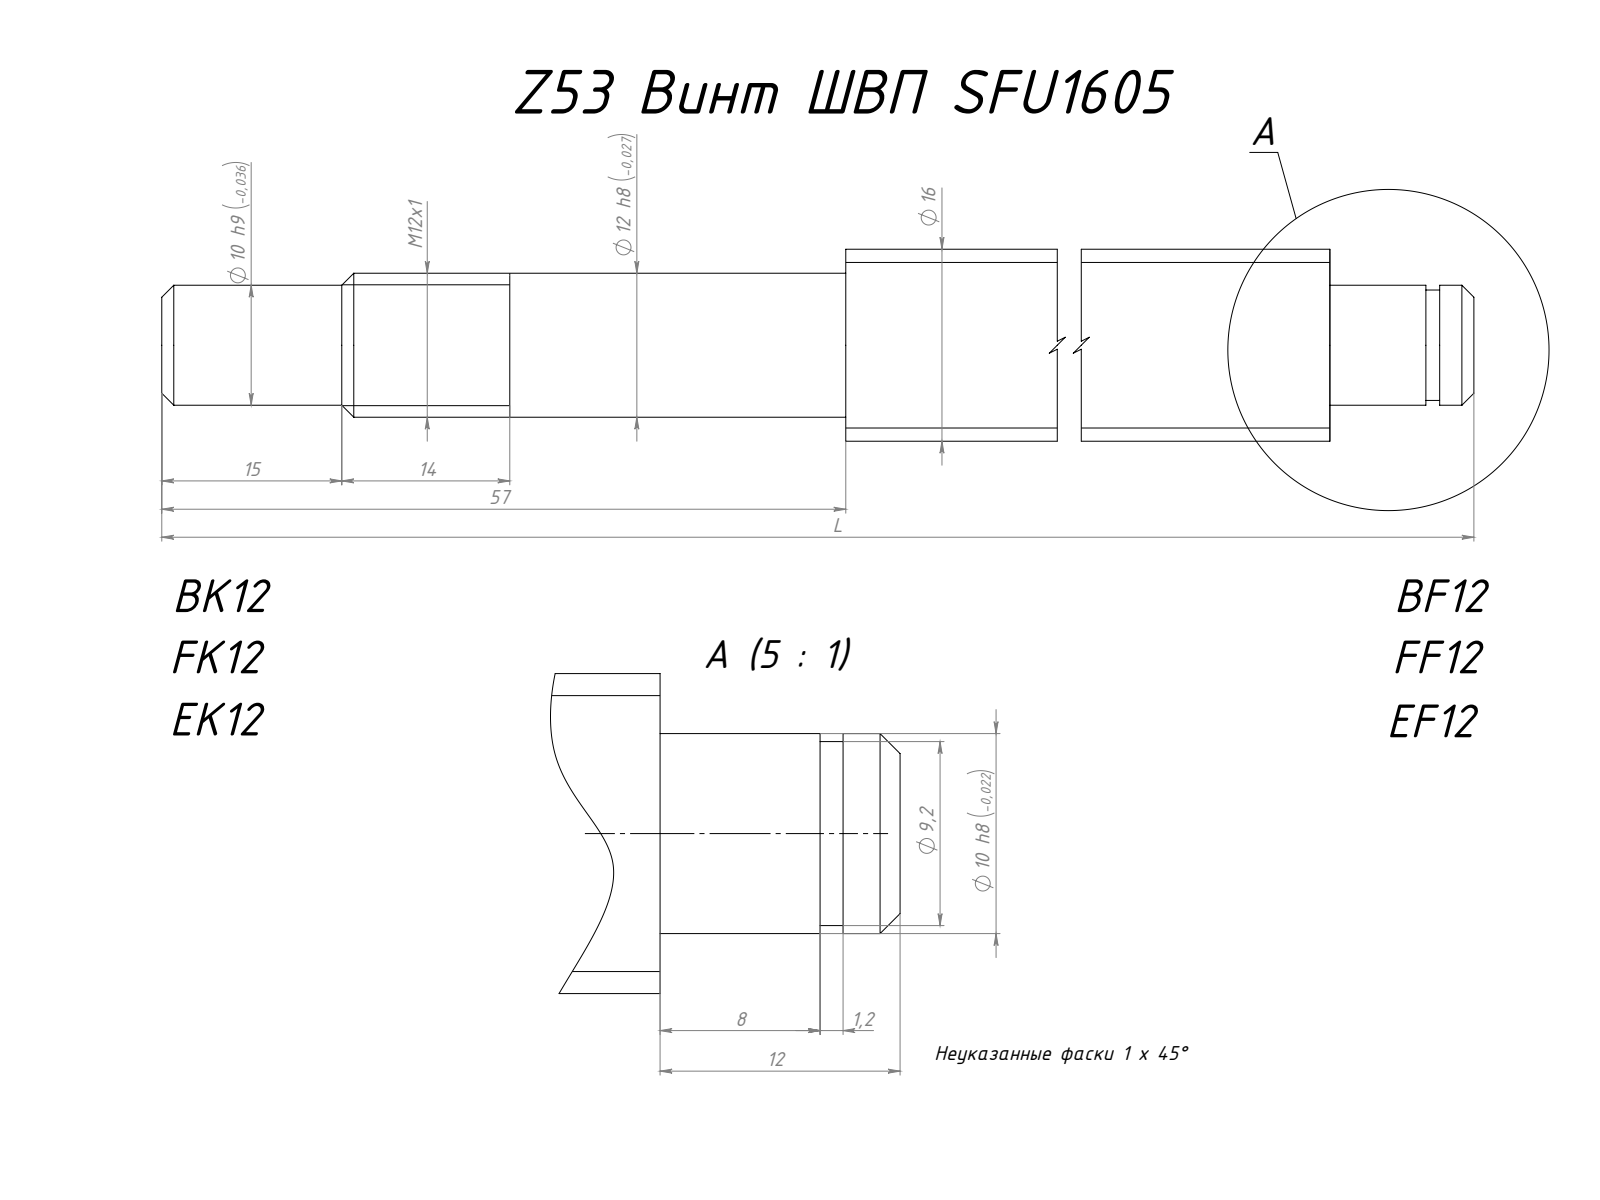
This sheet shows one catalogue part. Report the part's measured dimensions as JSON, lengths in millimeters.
{"part_name": "Z53 Винт ШВП SFU1605 - токарная обработка BK-BF, FK-FF, EK-EF-12", "step_written_by": "SolidWorks 2026 (AUTOMOTIVE_DESIGN)", "units": "millimeters", "bodies": {"solids": 1, "faces": 24, "planar": 6, "cylindrical": 12, "other": 6}, "overall_size": [3000, 16, 16], "volume_mm3": 596122, "surface_area_mm2": 150120, "round_bosses_or_shafts": [[16, 1], [12, 1], [10, 1], [9.2, 1]], "face_to_face_distances": [2931, 2943, 12, 57, 2988, 3000, 2996, 2997.15, 2939, 2940.15]}
